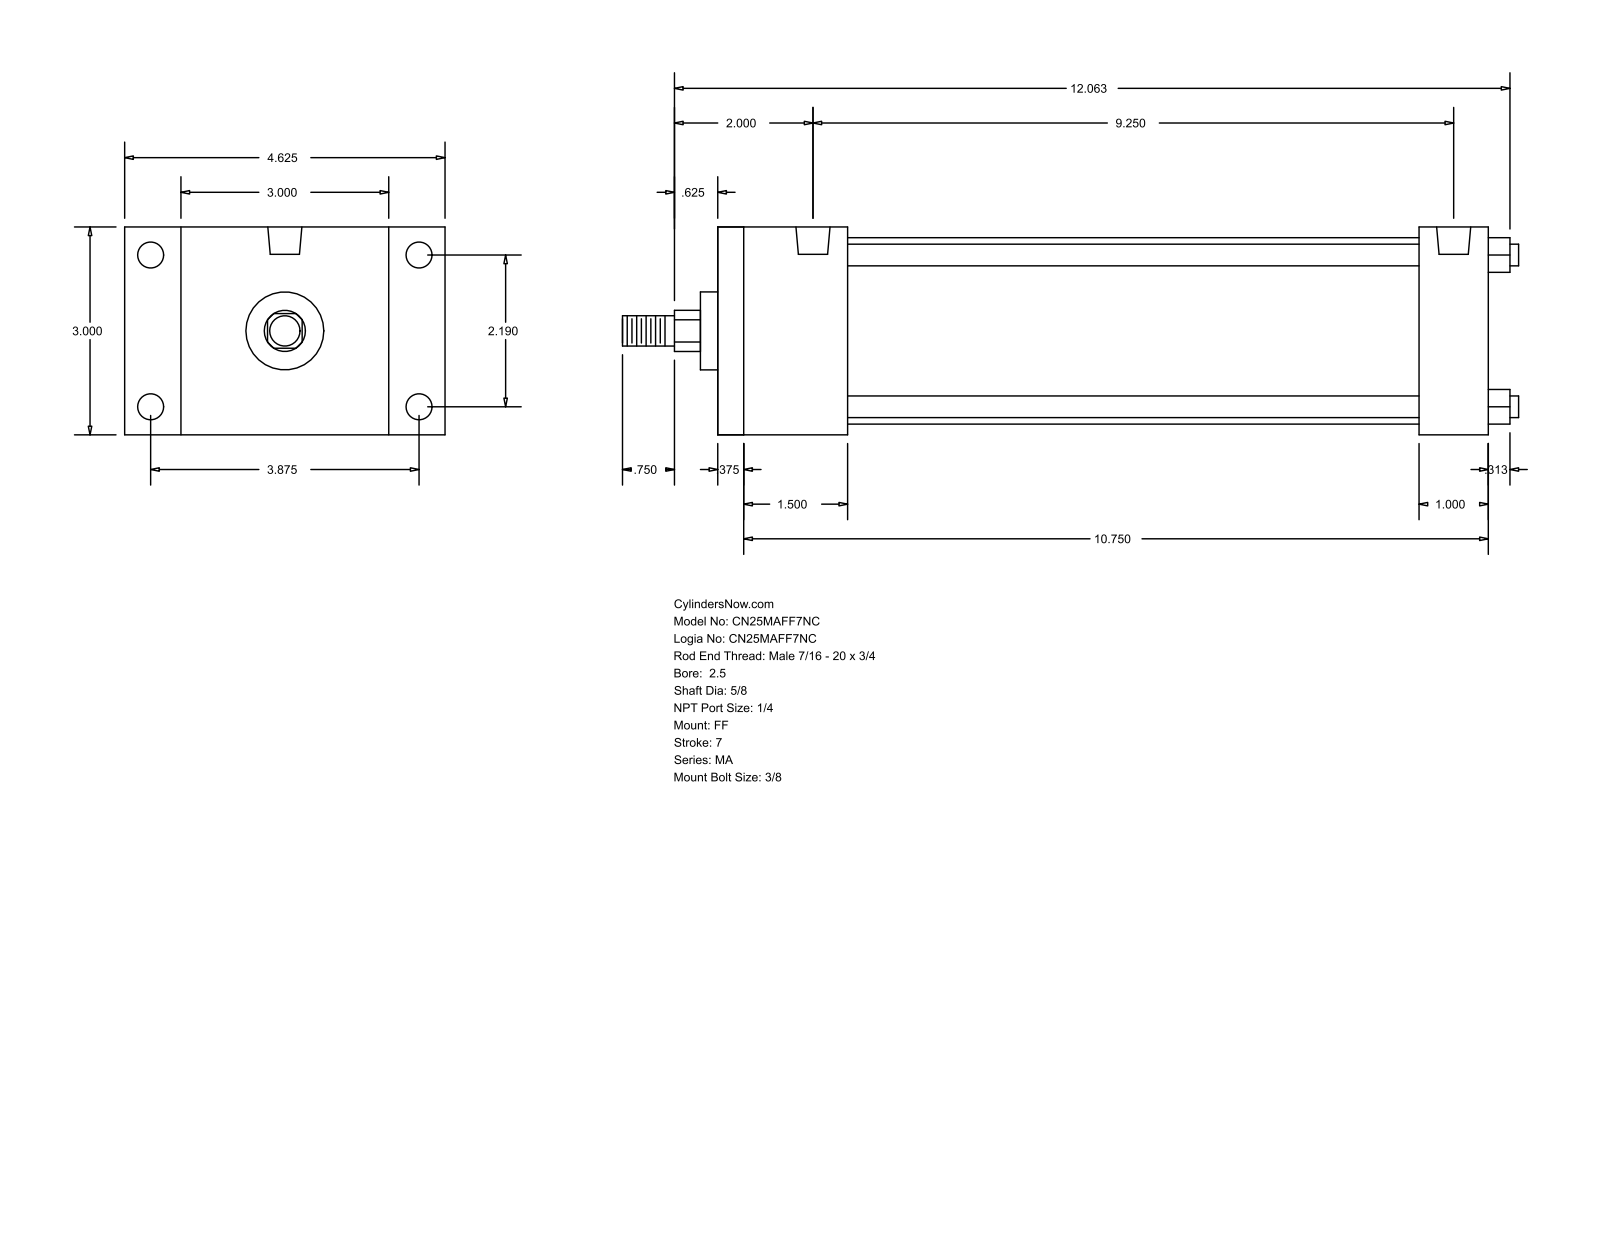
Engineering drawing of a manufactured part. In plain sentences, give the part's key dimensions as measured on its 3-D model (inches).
The part is named "MA_FF__0250_0.625". Its 3-D file was written by "GSSL Pune (CONFIG_CONTROL_DESIGN)". It is 0 solids with 92 faces: 64 planar, 28 cylindrical and 0 other. Overall it measures 12.937 by 4.625 by 3 inches. Round holes: 4 of diameter 0.313, 4 of diameter 0.375, 2 of diameter 0.492. Round bosses or shafts: 4 of diameter 0.313, 1 of diameter 2.69, 1 of diameter 1.125, 1 of diameter 0.625, 1 of diameter 0.437. Partial cylindrical surfaces (rounded edges, fillets, slot ends): 1 of radius 0.297. The main face-to-face distances are 3, 11.125, 10.75, 0.375, 1, 1.875, 10.125, 1.5, 9.75, 8.25. The hole center spacings are 2.19, 3.875, 4.451, 9.25.
